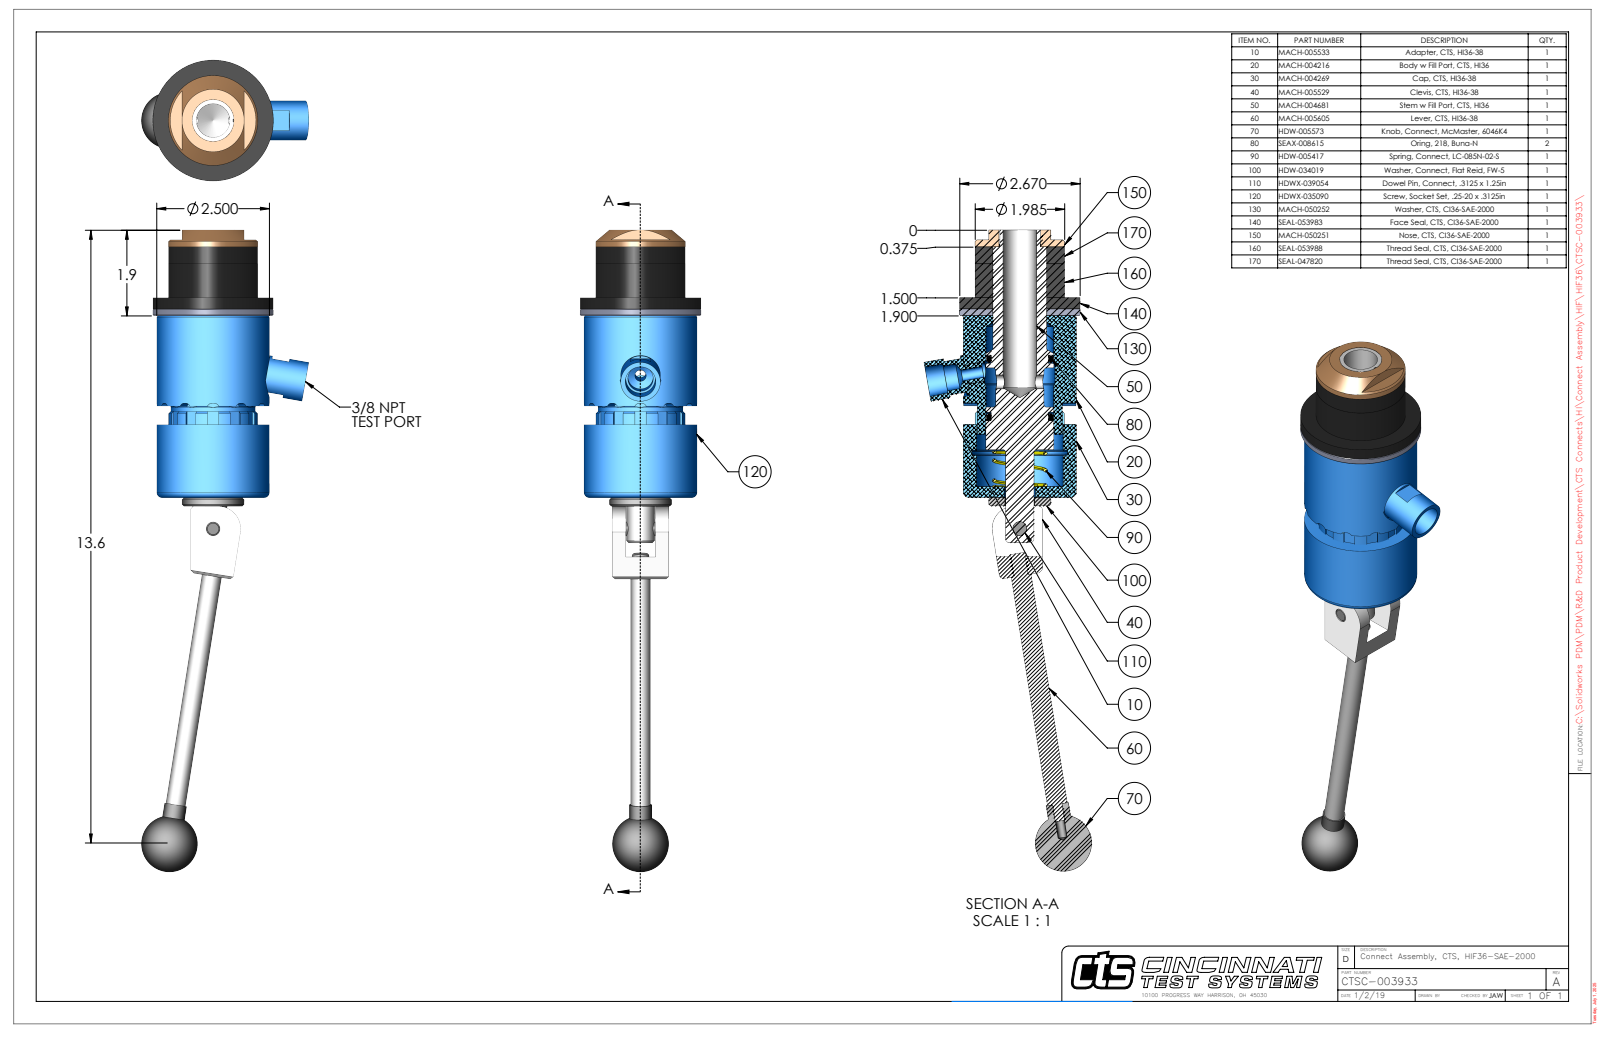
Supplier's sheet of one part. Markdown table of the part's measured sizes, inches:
| quantity | value |
| --- | --- |
| part name | CTSC-003933 |
| STEP written by | SolidWorks 2023 (AUTOMOTIVE_DESIGN) |
| units | inches |
| bodies | 11 solids, 401 faces (168 planar, 152 cylindrical, 81 other) |
| overall size | 14.215 × 3.716 × 2.675 |
| volume | 27.75 in³ |
| surface area | 147 in² |
| round holes (diameter × count) | 0.201 × 2, 0.15 × 1, 0.25 × 1, 0.311 × 1, 0.312 × 1, 0.313 × 1, 0.314 × 1, 0.562 × 1, 0.656 × 1, 0.696 × 1, 0.75 × 1, 0.922 × 1 |
| round bosses / shafts (diameter × count) | 2.675 × 1, 2.67 × 1, 2.5 × 1, 1.985 × 1, 1.98 × 1, 1.875 × 1, 1.38 × 1, 1.186 × 1 |
| partial cylindrical surfaces (radius × count) | 0.12 × 12, 0.029 × 2, 0.19 × 1, 0.195 × 1, 0.441 × 1, 0.47 × 1, 0.5 × 1, 0.961 × 1 |
| main face-to-face distances | 0.15, 0.25, 0.4, 0.75, 1.375, 1.125, 1.525, 4.03, 4.18, 4.43 |
| hole center spacings | 0.74, 2.118, 2.858 |
